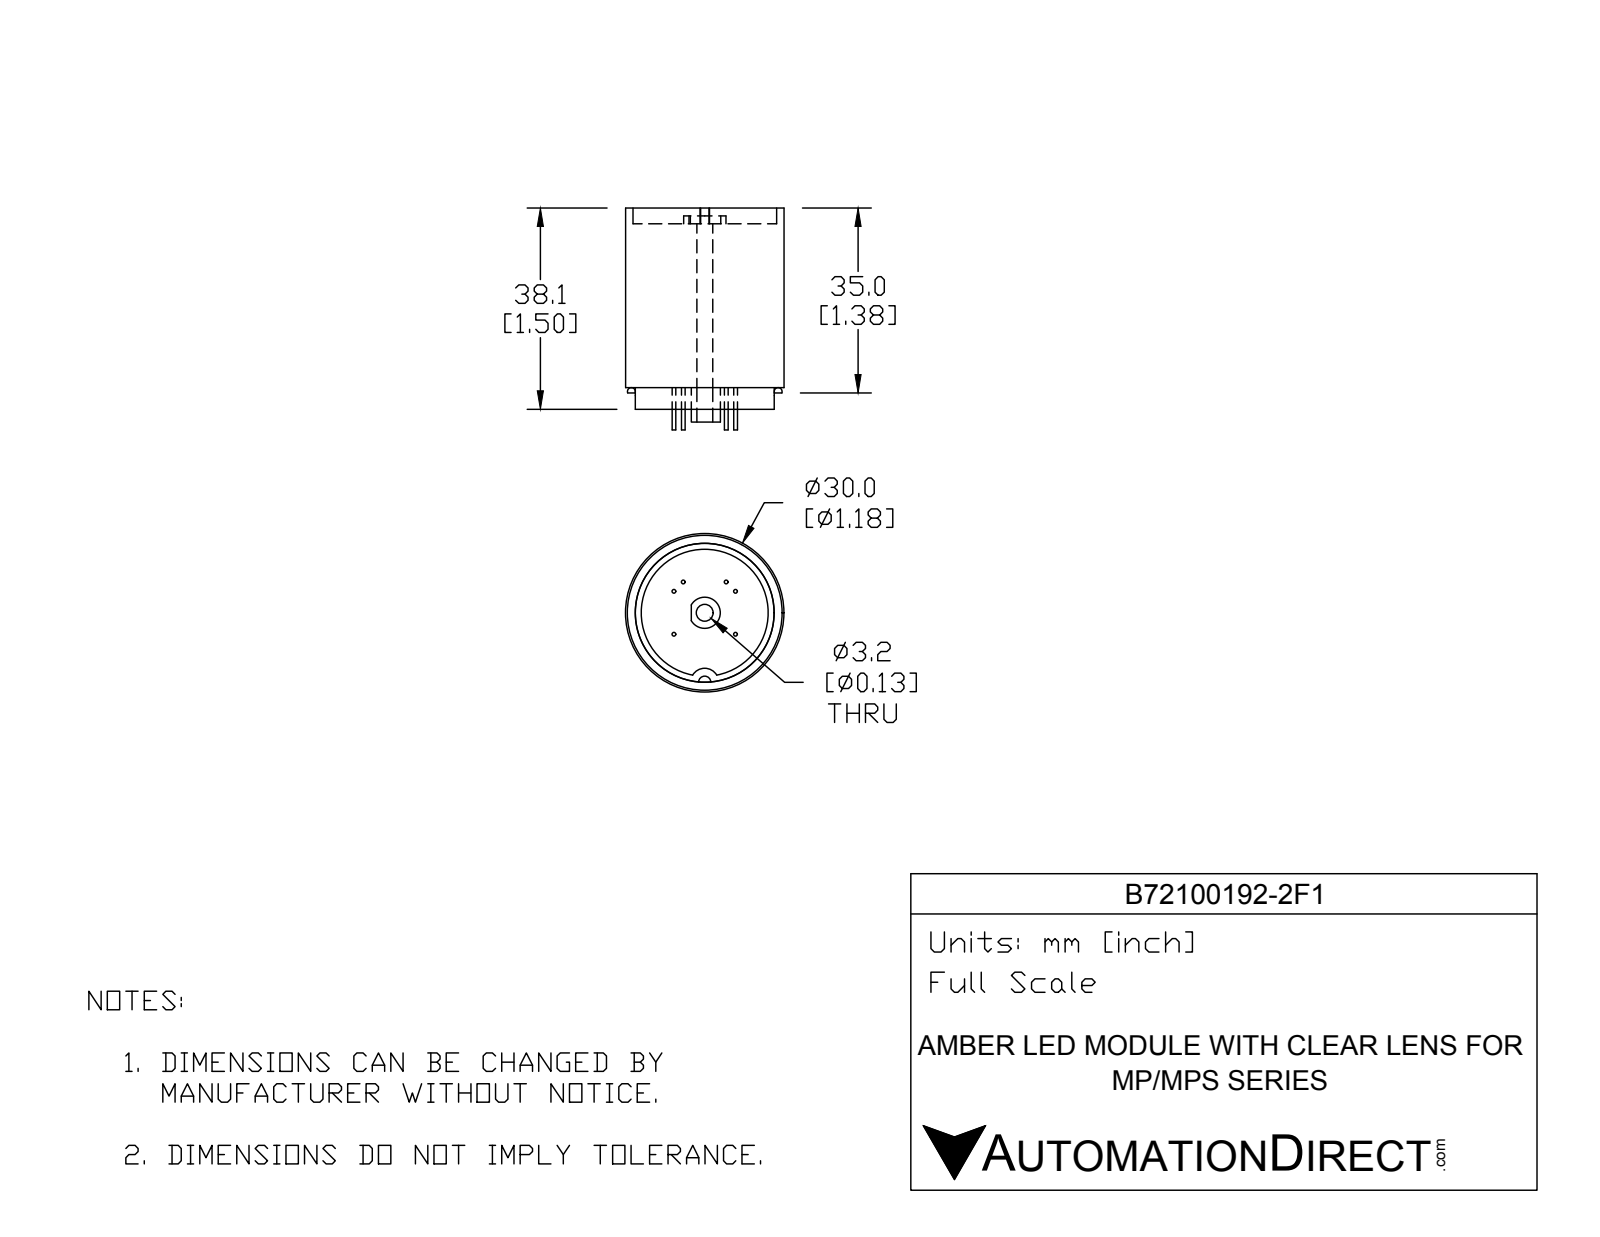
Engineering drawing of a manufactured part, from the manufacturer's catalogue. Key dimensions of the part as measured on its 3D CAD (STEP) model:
Part name (STEP PRODUCT): B72100192-2F1
STEP written by: SolidWorks 2016 (AUTOMOTIVE_DESIGN)
Units: millimetres
Bodies: 10 solids, 61 faces (25 planar, 32 cylindrical, 4 other)
Overall size (bounding box): 42 × 30 × 30
Volume: 22 770 mm³ · Surface area: 6 653 mm²
Round holes (diameter × count): ⌀3 ×1, ⌀6.06 ×1, ⌀24.04 ×1, ⌀27.2 ×1
Round bosses / shafts (diameter × count): ⌀0.7 ×6, ⌀30 ×1, ⌀26.3 ×1, ⌀8 ×1, ⌀5.9 ×1
Main face-to-face distances: 31, 34, 3, 4.1, 35.1, 38.1, 1.5, 36.6, 32.5, 2.42
